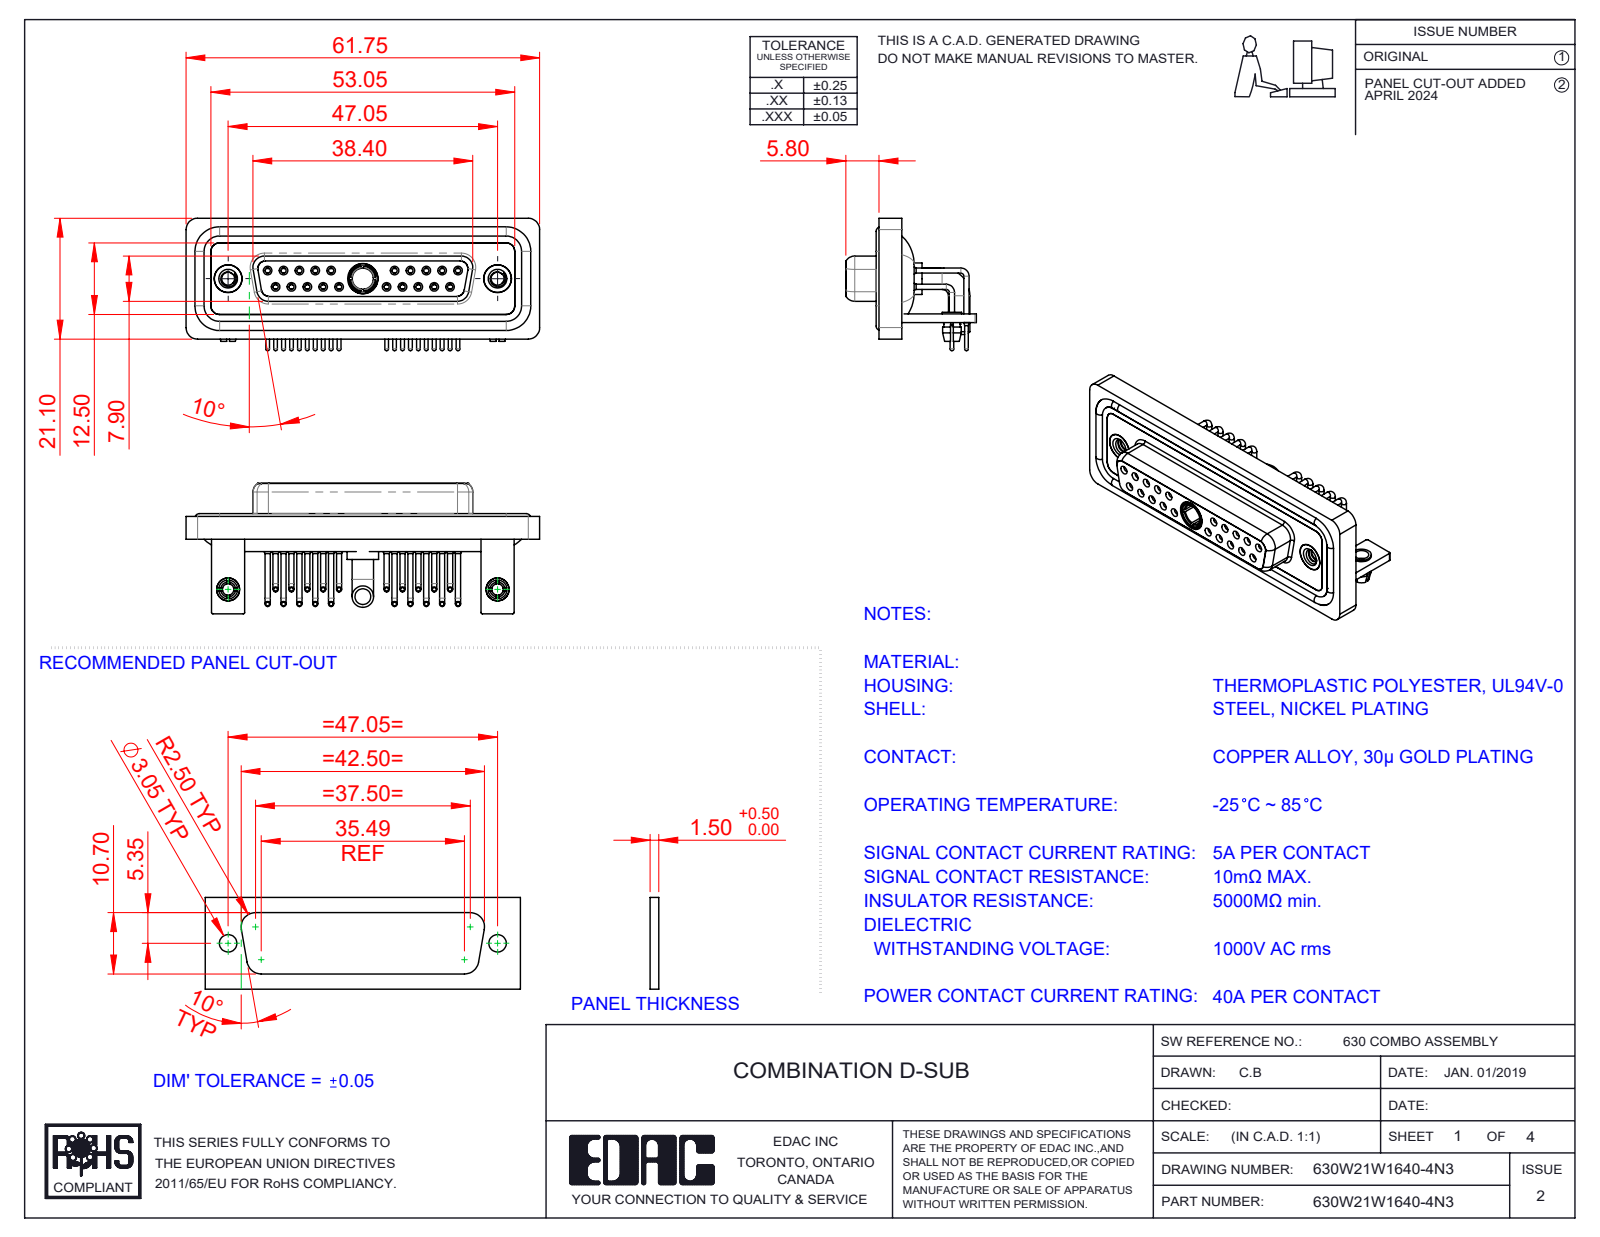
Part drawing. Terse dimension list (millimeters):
name: 630Combo Contact Row 1_50 Contacts; 630Combo Contact Row 2_50 Contacts; 630Combo Shell Rear_25 Contacts; 630W21W1640-4N3 (+7 more)
written by: SolidWorks 2023 (CONFIG_CONTROL_DESIGN)
unit: mm
bodies: 33 solids, 1664 faces (502 planar, 729 cylindrical, 433 other)
size: 61.75 × 23.12 × 22.8
volume: 8 981 mm³; area: 15 769 mm²
holes: 22× ⌀2, 20× ⌀0.9, 20× ⌀1.1, 20× ⌀1.5, 10× ⌀1.6, 10× ⌀1.7, 3× ⌀4.85, 2× ⌀2.26, 2× ⌀2.5, 2× ⌀3.2, 2× ⌀4, 2× ⌀4.05
bosses: 20× ⌀0.9, 20× ⌀0.65, 14× ⌀1.6, 2× ⌀4.95, 2× ⌀4.8, 2× ⌀4, 2× ⌀3.75, 2× ⌀3.4
rounds: 19× R2, 18× R1.5, 16× R0.25, 8× R1.35, 8× R1.6, 5× R0.5, 4× R0.6, 4× R0.65
face distances: 0.4, 1.8, 2.9, 3.7, 1.5, 4.1, 1.1, 1.4, 1.6, 2.5
hole spacings: 3.16, 2.77, 5.54, 8.31, 5.04, 19.39, 20.97, 22.16
